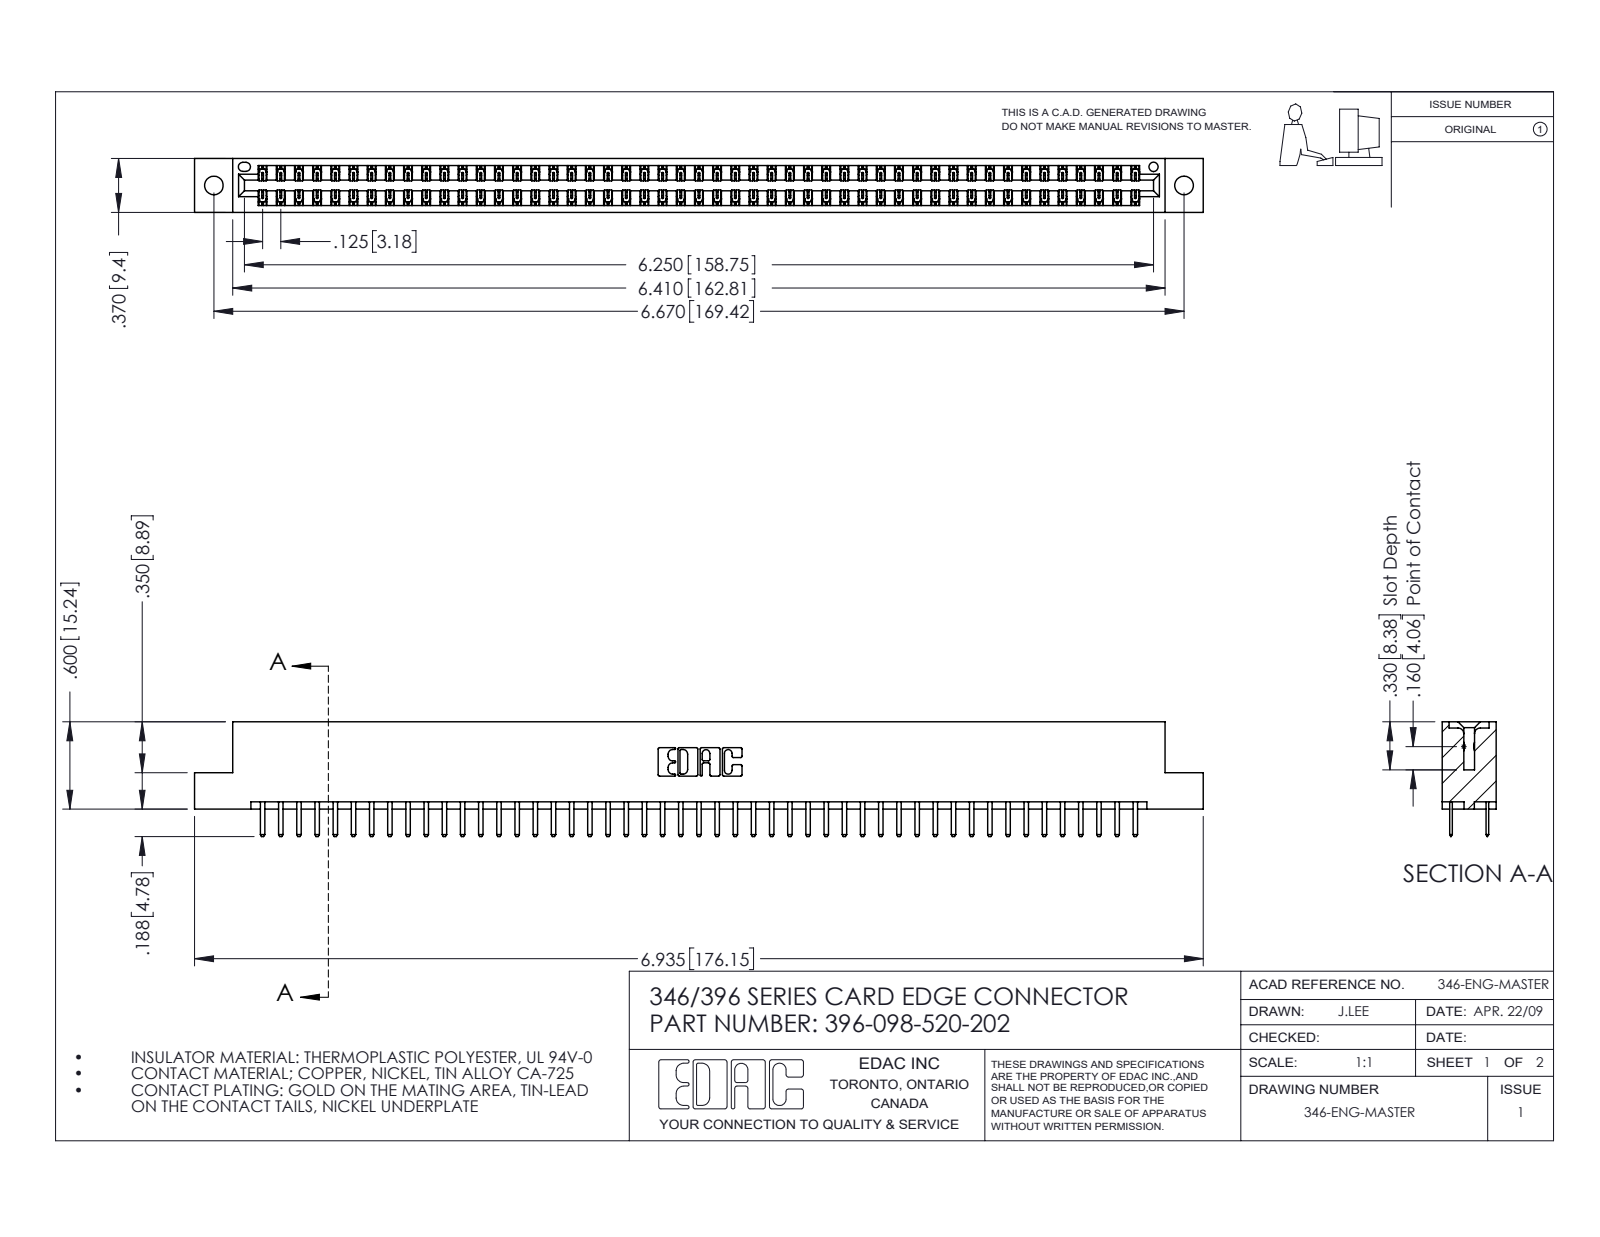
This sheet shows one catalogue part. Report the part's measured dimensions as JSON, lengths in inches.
{"part_name": "345-292-001_345-293-120; 396-098-520-202; 346 Part_Flush Mounting Lugs - 0.128 Dia", "step_written_by": "SolidWorks 2016 (CONFIG_CONTROL_DESIGN)", "units": "inches", "bodies": {"solids": 99, "faces": 5610, "planar": 3702, "cylindrical": 1908, "other": 0}, "overall_size": [6.935, 0.788, 0.37], "volume_in3": 1.047, "surface_area_in2": 36.14, "round_holes": [[0.128, 2], [0.064, 1]], "partial_cylinders_radius": [[0.006, 147], [0.01, 102], [0.01, 22], [0.007, 6], [0.031, 6], [0.026, 3], [0.014, 2], [0.022, 2]], "face_to_face_distances": [0.048, 0.322, 0.25, 0.37, 0.275, 0.072, 0.298, 0.025, 0.148, 0.222], "hole_center_spacings": [0.246, 6.461, 6.67]}
